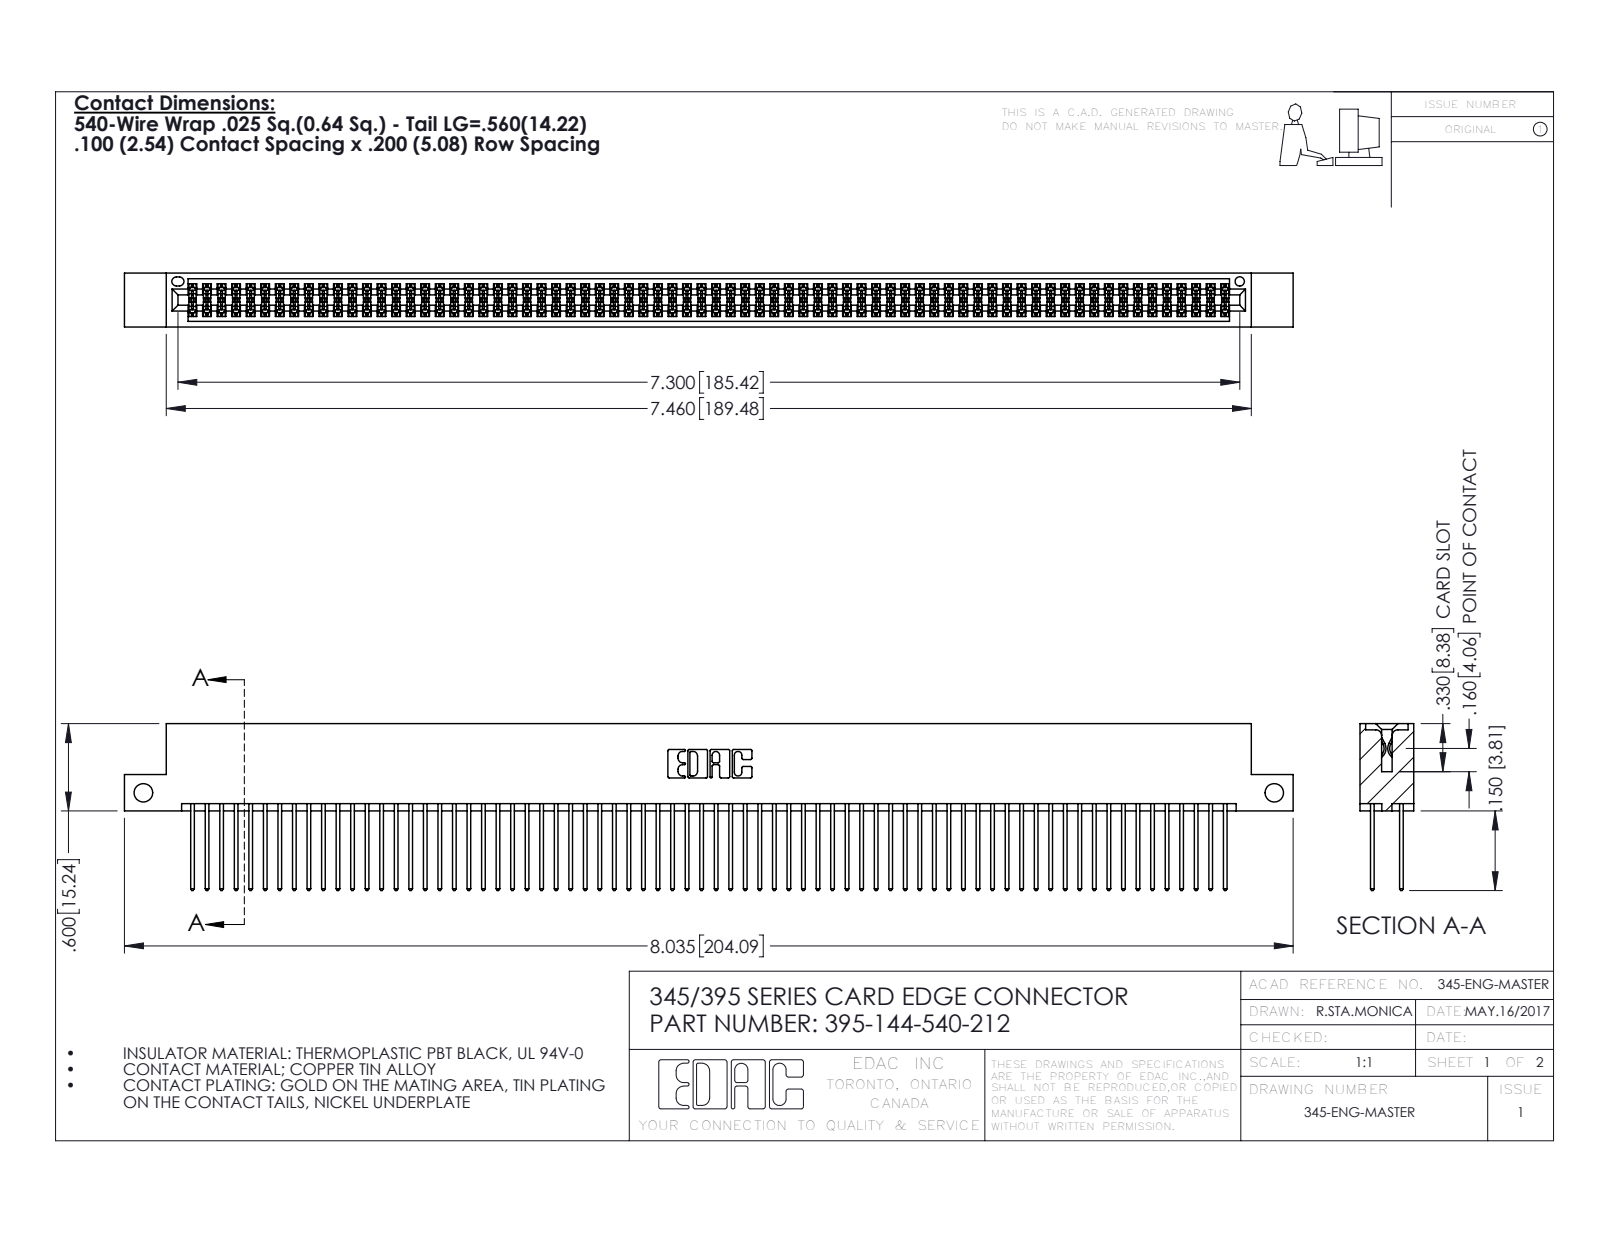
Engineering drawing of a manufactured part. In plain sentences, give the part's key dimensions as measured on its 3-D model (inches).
The part is named "345-292-001_345-293-140; 345 Part_Flush Mounting Lugs - Side Mount; 395-144-540-212". Its 3-D file was written by "SolidWorks 2016 (CONFIG_CONTROL_DESIGN)". It is 145 solids with 7326 faces: 4832 planar, 2494 cylindrical and 0 other. Overall it measures 8.035 by 1.147 by 0.37 inches. Its volume is 1.255 cubic inches and its surface area 51.73 square inches. Round holes: 2 of diameter 0.128, 1 of diameter 0.064. Partial cylindrical surfaces (rounded edges, fillets, slot ends): 216 of radius 0.006, 144 of radius 0.01, 22 of radius 0.01, 6 of radius 0.007, 6 of radius 0.031, 3 of radius 0.026, 2 of radius 0.014, 2 of radius 0.019. The main face-to-face distances are 0.298, 0.072, 0.2, 0.098, 0.272, 0.025, 0.225, 0.37, 0.175, 0.149. The hole center spacings are 7.775.
